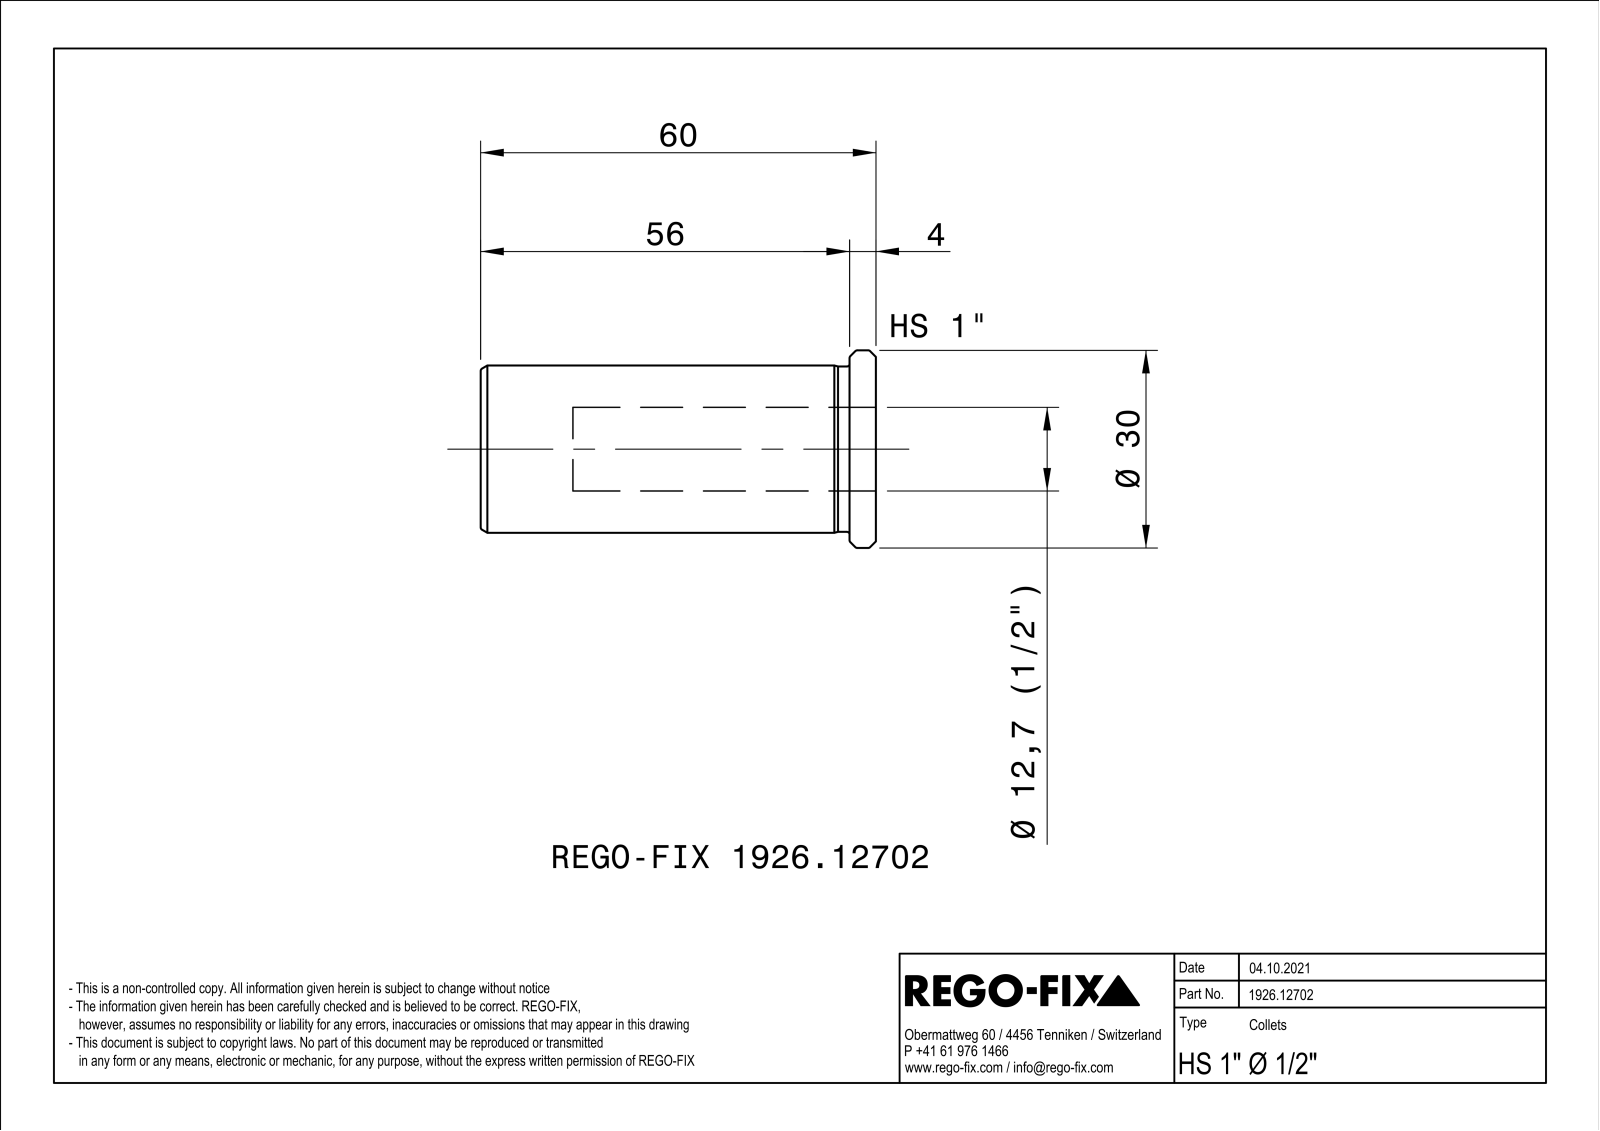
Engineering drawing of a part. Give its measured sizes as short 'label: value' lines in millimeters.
name: NOCUT
written by: SIEMENS PLM Software Solid Edge ST10 (AUTOMOTIVE_DESIGN)
unit: mm
bodies: 1 solid, 70 faces (22 planar, 11 cylindrical, 37 other)
size: 60 × 29.98 × 29.98
volume: 20 067 mm³; area: 10 114 mm²
holes: 1× ⌀12.7, 1× ⌀20.5
bosses: 1× ⌀30, 1× ⌀25.4, 1× ⌀25.1
face distances: 1, 60, 4, 56
